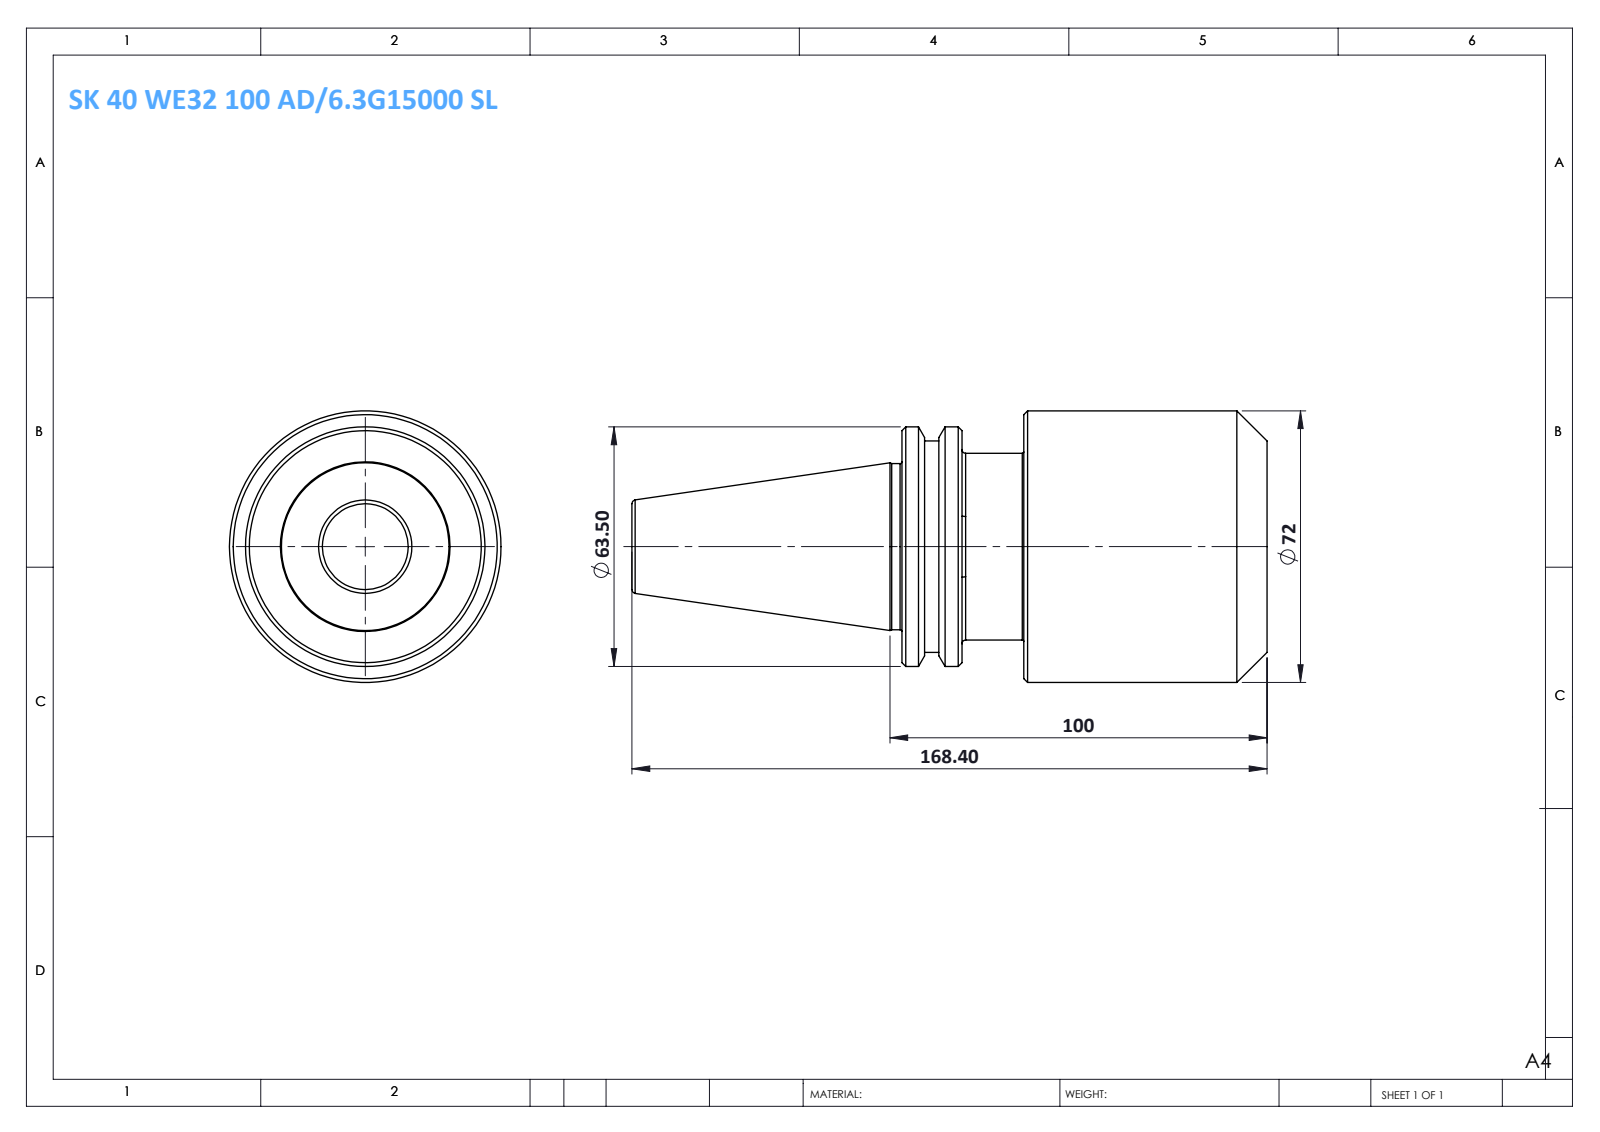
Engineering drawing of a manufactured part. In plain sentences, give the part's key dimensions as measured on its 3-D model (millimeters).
The part is named "SK40 WE32 100 AD-6.3G15000 SL". Its 3-D file was written by "SolidWorks 2014 (CONFIG_CONTROL_DESIGN)". It is 1 solid with 44 faces: 8 planar, 12 cylindrical and 24 other. Overall it measures 168.4 by 72 by 72 millimeters. Its volume is 404 495 cubic millimeters and its surface area 37 010 square millimeters. Round bosses or shafts: 1 of diameter 72, 1 of diameter 63.5, 1 of diameter 56, 1 of diameter 49.5, 1 of diameter 44. The main face-to-face distances are 64.5, 96.8, 32.3, 80.9, 16.4, 15.9, 168.4, 103.9, 87.5, 71.6.
